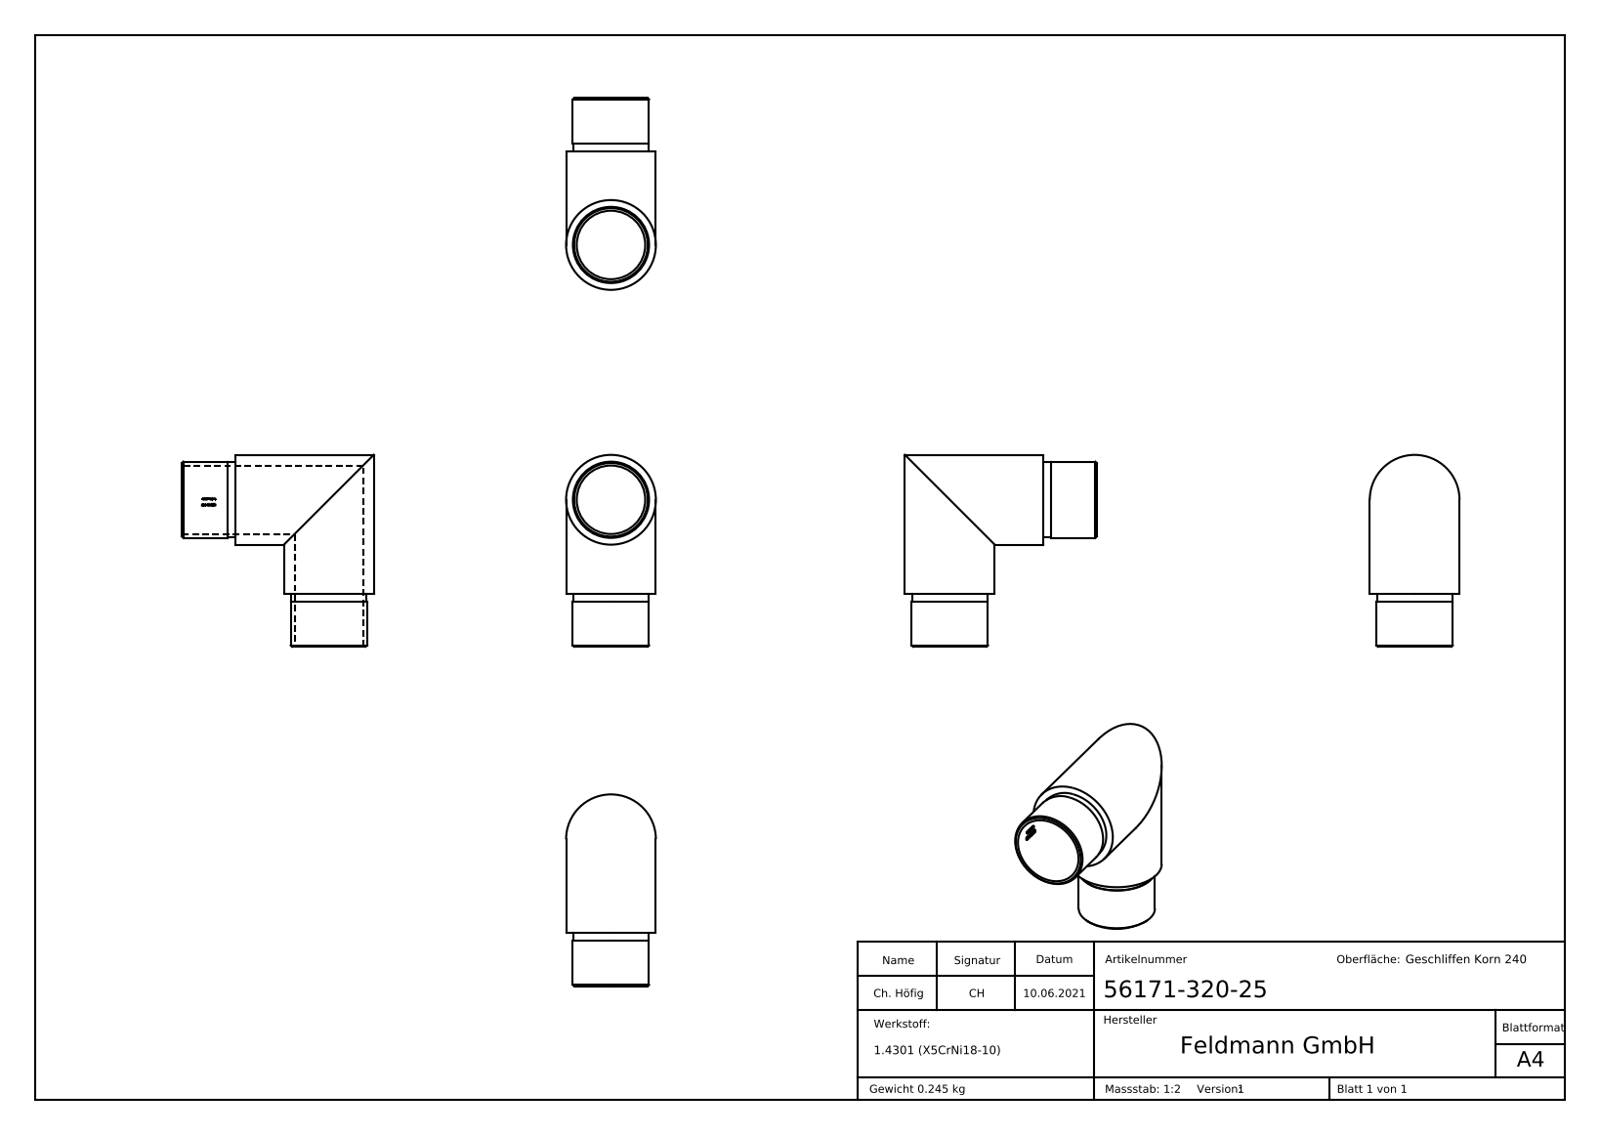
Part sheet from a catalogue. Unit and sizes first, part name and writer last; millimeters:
Units: millimetres
Overall size (bounding box): 72 × 72 × 33.7
Round holes (diameter × count): ⌀25.7 ×2
Round bosses / shafts (diameter × count): ⌀33.7 ×2, ⌀28.6 ×2, ⌀28.2 ×2
Partial cylindrical surfaces — rounded edges, fillets, slot ends (radius × count): R12.95 ×1
Main face-to-face distances: 20, 17, 3, 0.71, 0.79, 0.83, 1.88, 2.45, 0.56, 0.66
Volume: 31 055 mm³ · Surface area: 20 706 mm²
Bodies: 1 solid, 269 faces (116 planar, 41 cylindrical, 112 other)
Part name (STEP PRODUCT): 56171-320-25
STEP written by: SolidWorks 2018 (CONFIG_CONTROL_DESIGN)
